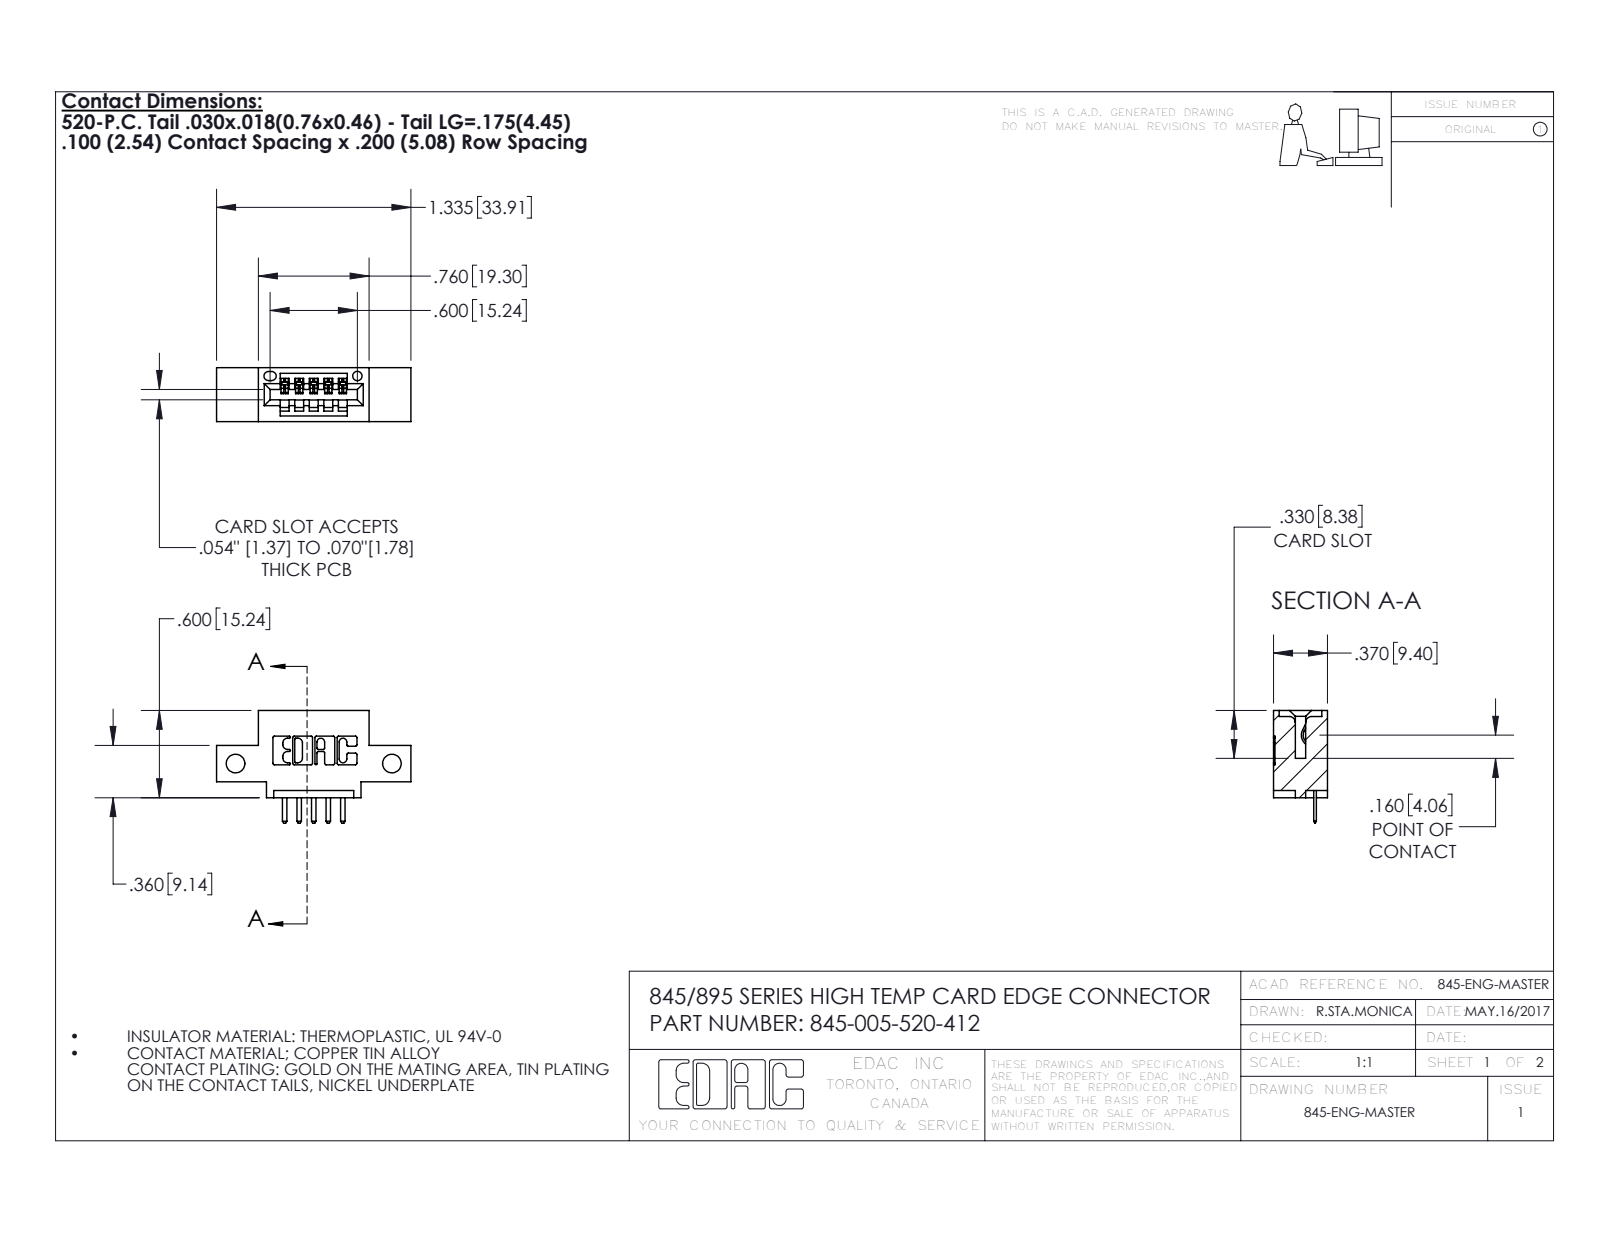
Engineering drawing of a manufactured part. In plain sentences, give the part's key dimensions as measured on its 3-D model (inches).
The part is named "345 Part_0.110 Offset - Side Mount; 345-005-520-412; 345-292-001_345-293-120". Its 3-D file was written by "SolidWorks 2016 (CONFIG_CONTROL_DESIGN)". It is 6 solids with 440 faces: 294 planar, 146 cylindrical and 0 other. Overall it measures 1.335 by 0.775 by 0.37 inches. Its volume is 0.167 cubic inches and its surface area 4.704 square inches. Round holes: 2 of diameter 0.128, 1 of diameter 0.064. Partial cylindrical surfaces (rounded edges, fillets, slot ends): 22 of radius 0.01, 12 of radius 0.01, 10 of radius 0.006, 6 of radius 0.007, 6 of radius 0.031, 3 of radius 0.026, 2 of radius 0.031, 2 of radius 0.04. The main face-to-face distances are 0.2, 0.37, 0.1, 0.298, 0.072, 0.25, 0.025, 0.06, 0.16, 0.55. The hole center spacings are 1.075.
